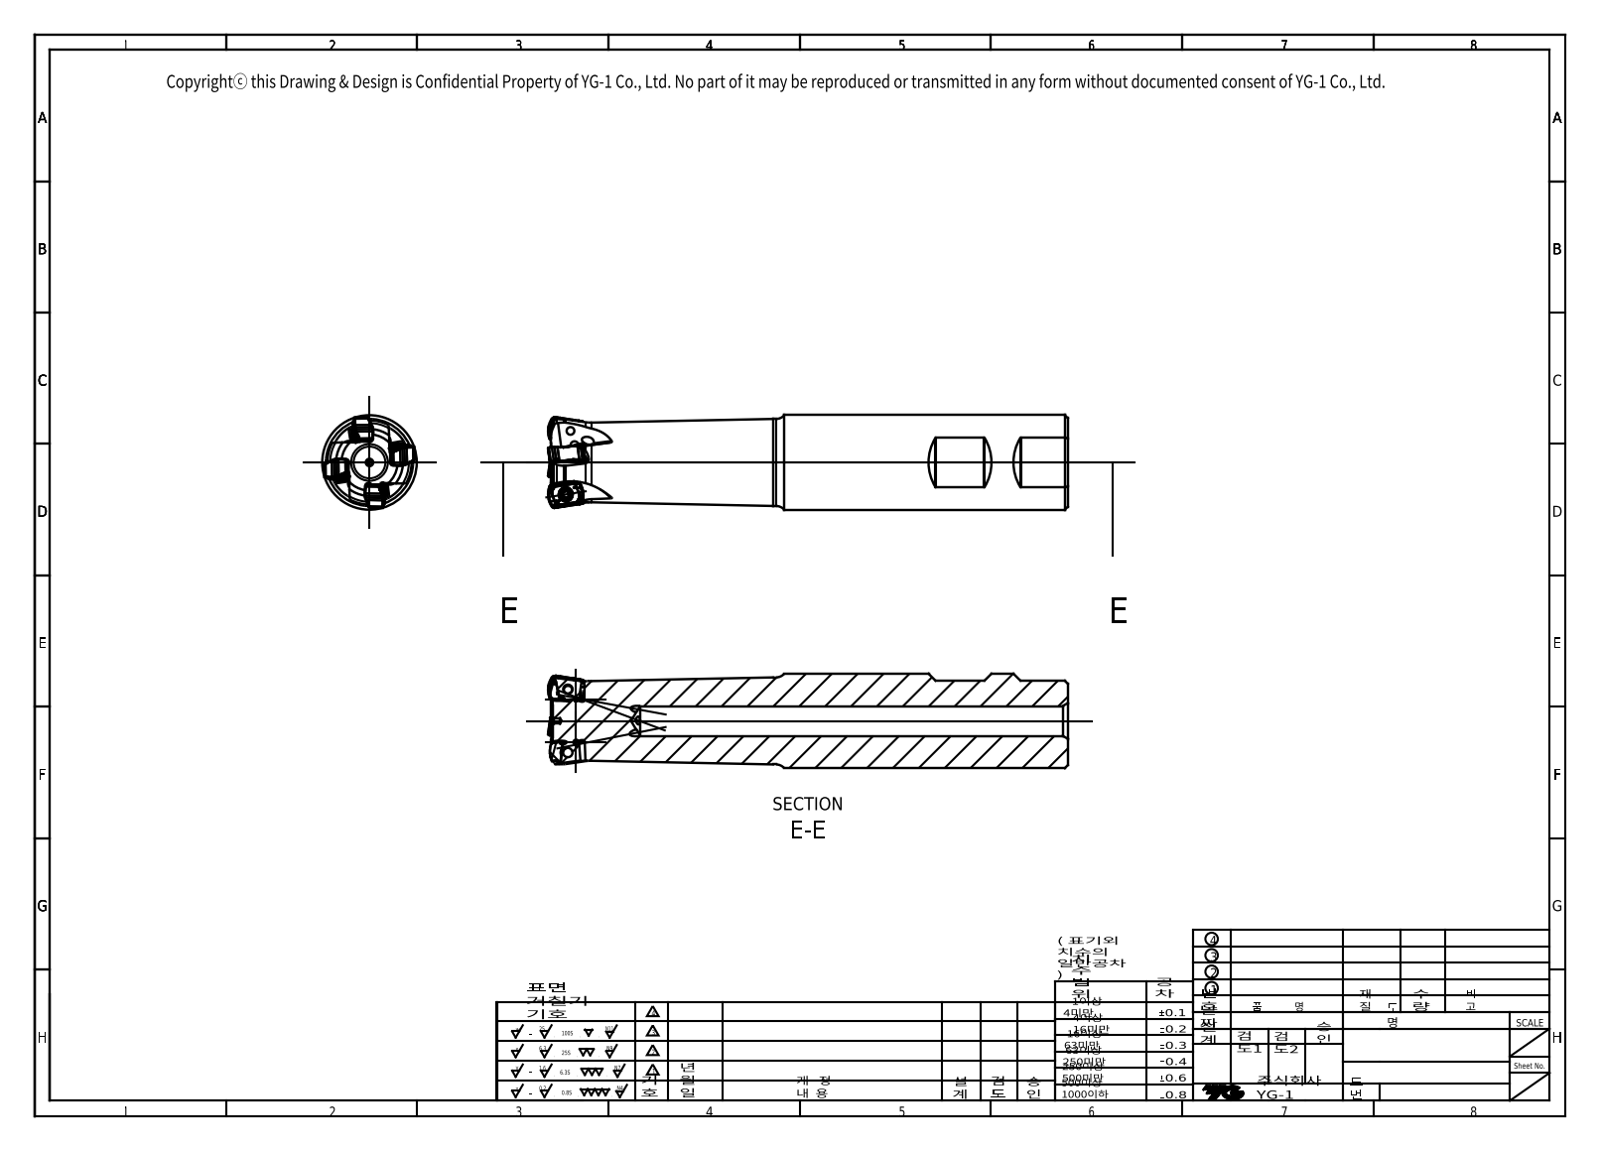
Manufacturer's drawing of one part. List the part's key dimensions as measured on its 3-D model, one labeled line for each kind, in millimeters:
Part name (STEP PRODUCT): 1201030C7DCCgc08
STEP written by: SIEMENS PLM Software NX 10.0 (AP203_CONFIGURATION_CONTROLLED_3D_DESIGN_OF_MECHANICAL_PARTS_AND_ASSEMBLIES_MIM_LF)
Units: millimetres
Bodies: 2 solids, 61 faces (8 planar, 6 cylindrical, 47 other)
Overall size (bounding box): 139.7 × 25.43 × 25.43
Round holes (diameter × count): ⌀8 ×1
Round bosses / shafts (diameter × count): ⌀25.4 ×1, ⌀23.4 ×1
Partial cylindrical surfaces — rounded edges, fillets, slot ends (radius × count): R0.3 ×3
Main face-to-face distances: 138.7, 16.14, 24.55, 8.41
